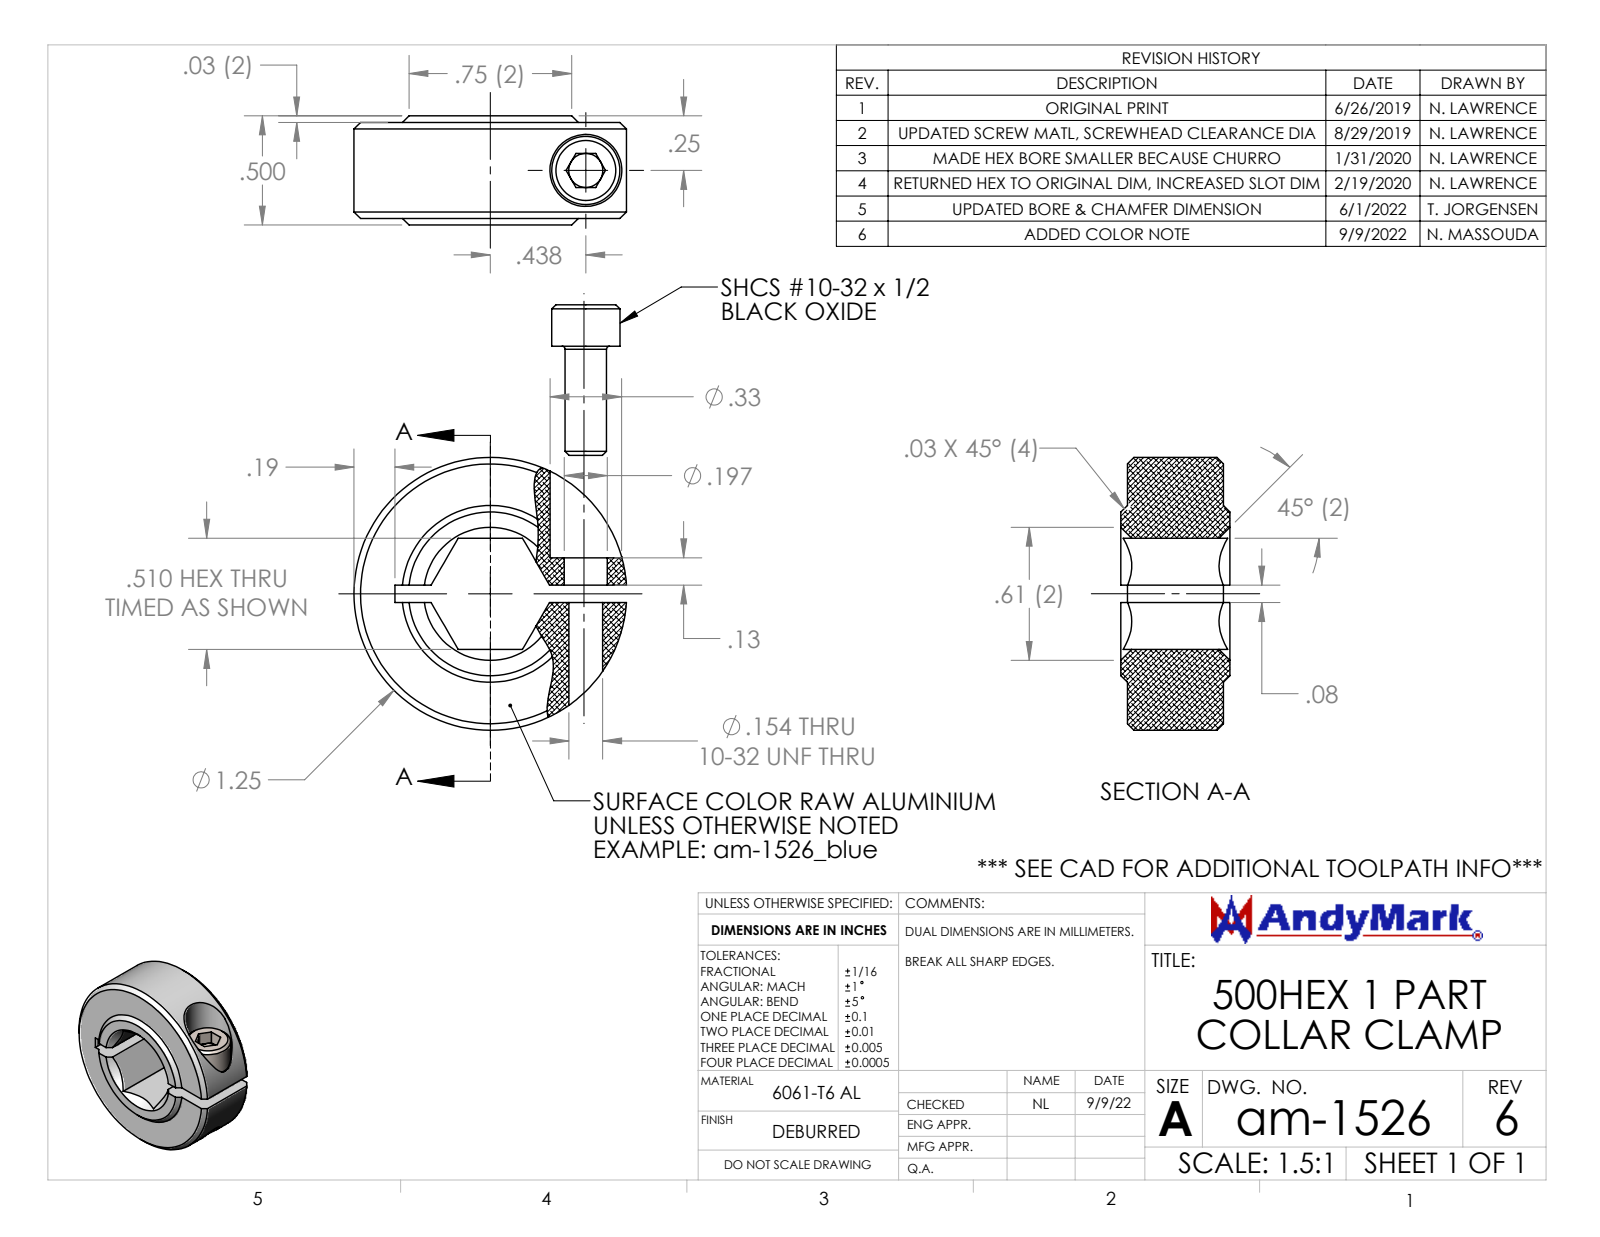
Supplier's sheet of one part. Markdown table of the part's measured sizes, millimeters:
| quantity | value |
| --- | --- |
| part name | 10-32x0500_shcs_HX-SHCS 0.19-32x1.375x1-C; am-1526 500Hex Collar Clamp; 500Hex Collar Clamp Body |
| STEP written by | SolidWorks 2022 (CONFIG_CONTROL_DESIGN) |
| units | millimeters |
| bodies | 2 solids, 64 faces (33 planar, 12 cylindrical, 19 other) |
| overall size | 31.75 × 31.72 × 12.7 |
| volume | 6 936 mm³ |
| surface area | 3 751 mm² |
| round holes (diameter × count) | 4.04 × 1, 5.11 × 1, 8.38 × 1 |
| round bosses / shafts (diameter × count) | 31.75 × 1, 7.94 × 1, 4.83 × 1 |
| main face-to-face distances | 11.18, 12.95, 0.76, 11.94, 5.46, 7.49, 2.03, 12.7, 2.29, 10.66 |
